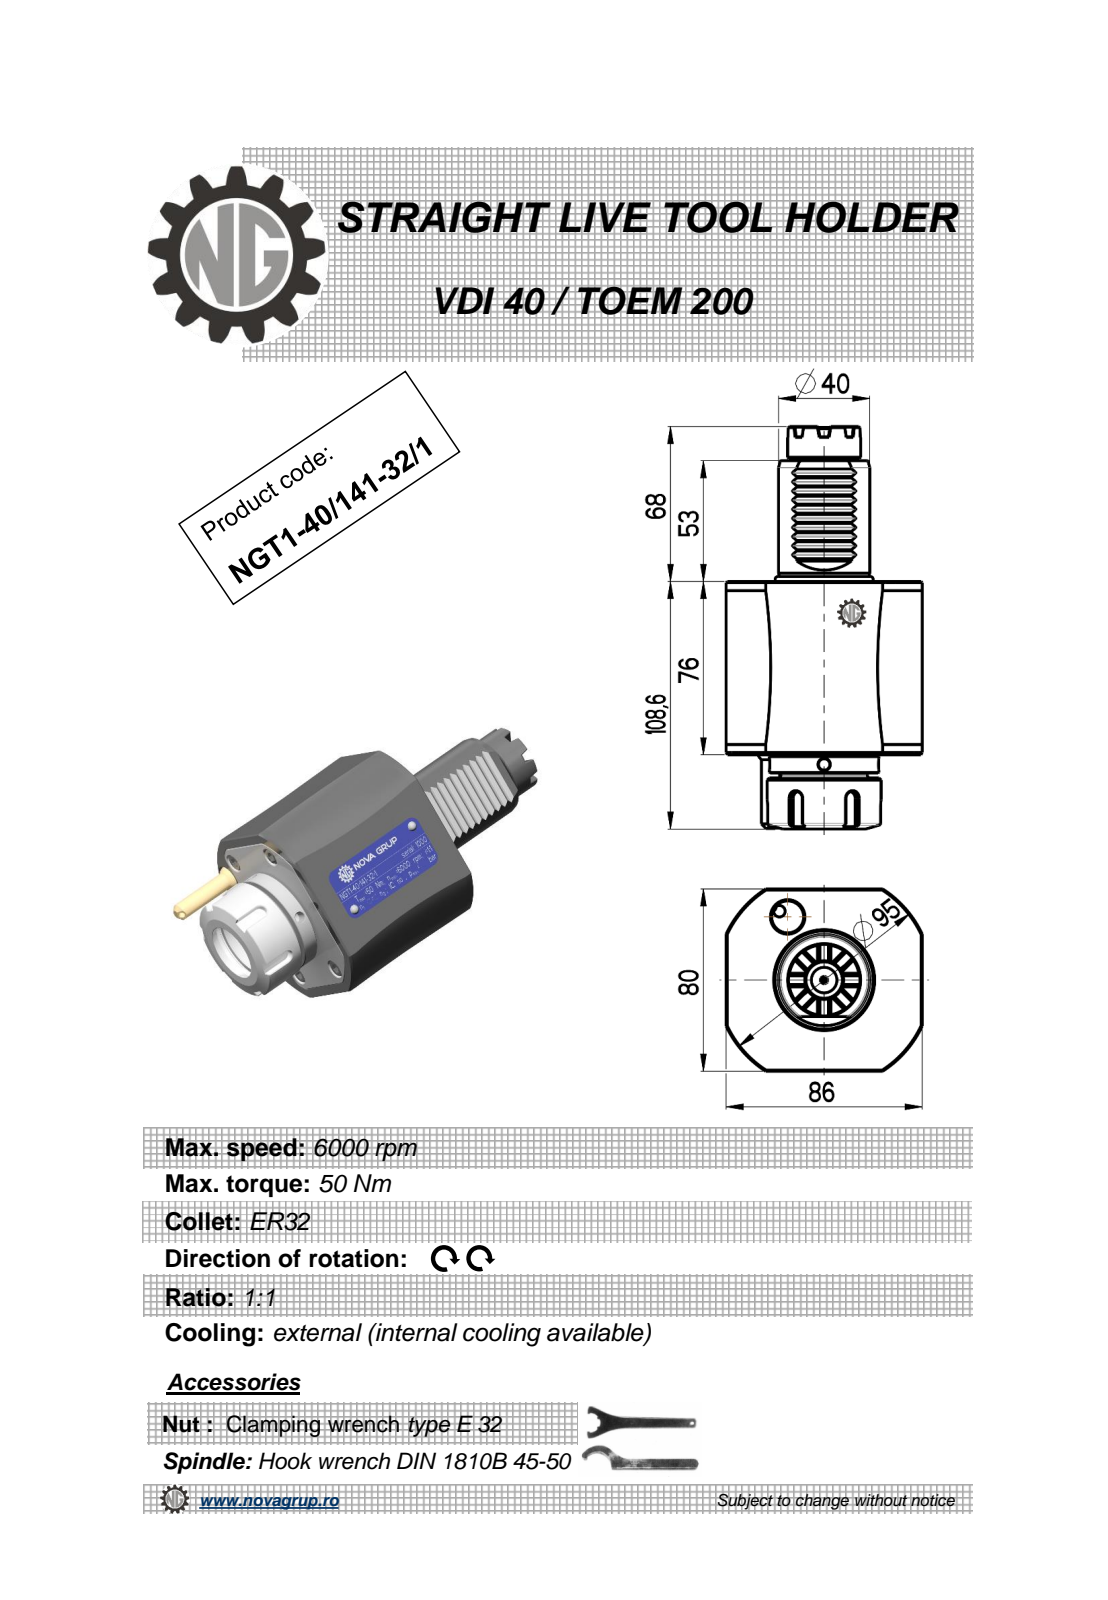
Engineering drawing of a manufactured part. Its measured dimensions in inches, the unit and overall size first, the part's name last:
Units: inches
Overall size (bounding box): 6.953 × 3.386 × 3.213
Round holes (diameter × count): ⌀0.197 ×3, ⌀0.118 ×1, ⌀1.063 ×1
Round bosses / shafts (diameter × count): ⌀1.969 ×1, ⌀1.89 ×1, ⌀1.634 ×1, ⌀1.614 ×1, ⌀1.575 ×1, ⌀1.26 ×1, ⌀0.677 ×1, ⌀0.315 ×1
Partial cylindrical surfaces — rounded edges, fillets, slot ends (radius × count): R0.012 ×10, R0.009 ×6, R0.118 ×5, R1.87 ×1
Main face-to-face distances: 2.992, 3.15, 3.386, 0.111, 4.098, 1.106, 0.223, 0.177, 2.087, 5.079
Hole centre spacings: 1.575
Volume: 36.91 in³ · Surface area: 82.66 in²
Bodies: 1 solid, 330 faces (141 planar, 64 cylindrical, 125 other)
Part name (STEP PRODUCT): NGT1_40_141_32_1
STEP written by: PRO/ENGINEER BY PARAMETRIC TECHNOLOGY CORPORATION, 2010280 (CONFIG_CONTROL_DESIGN)
